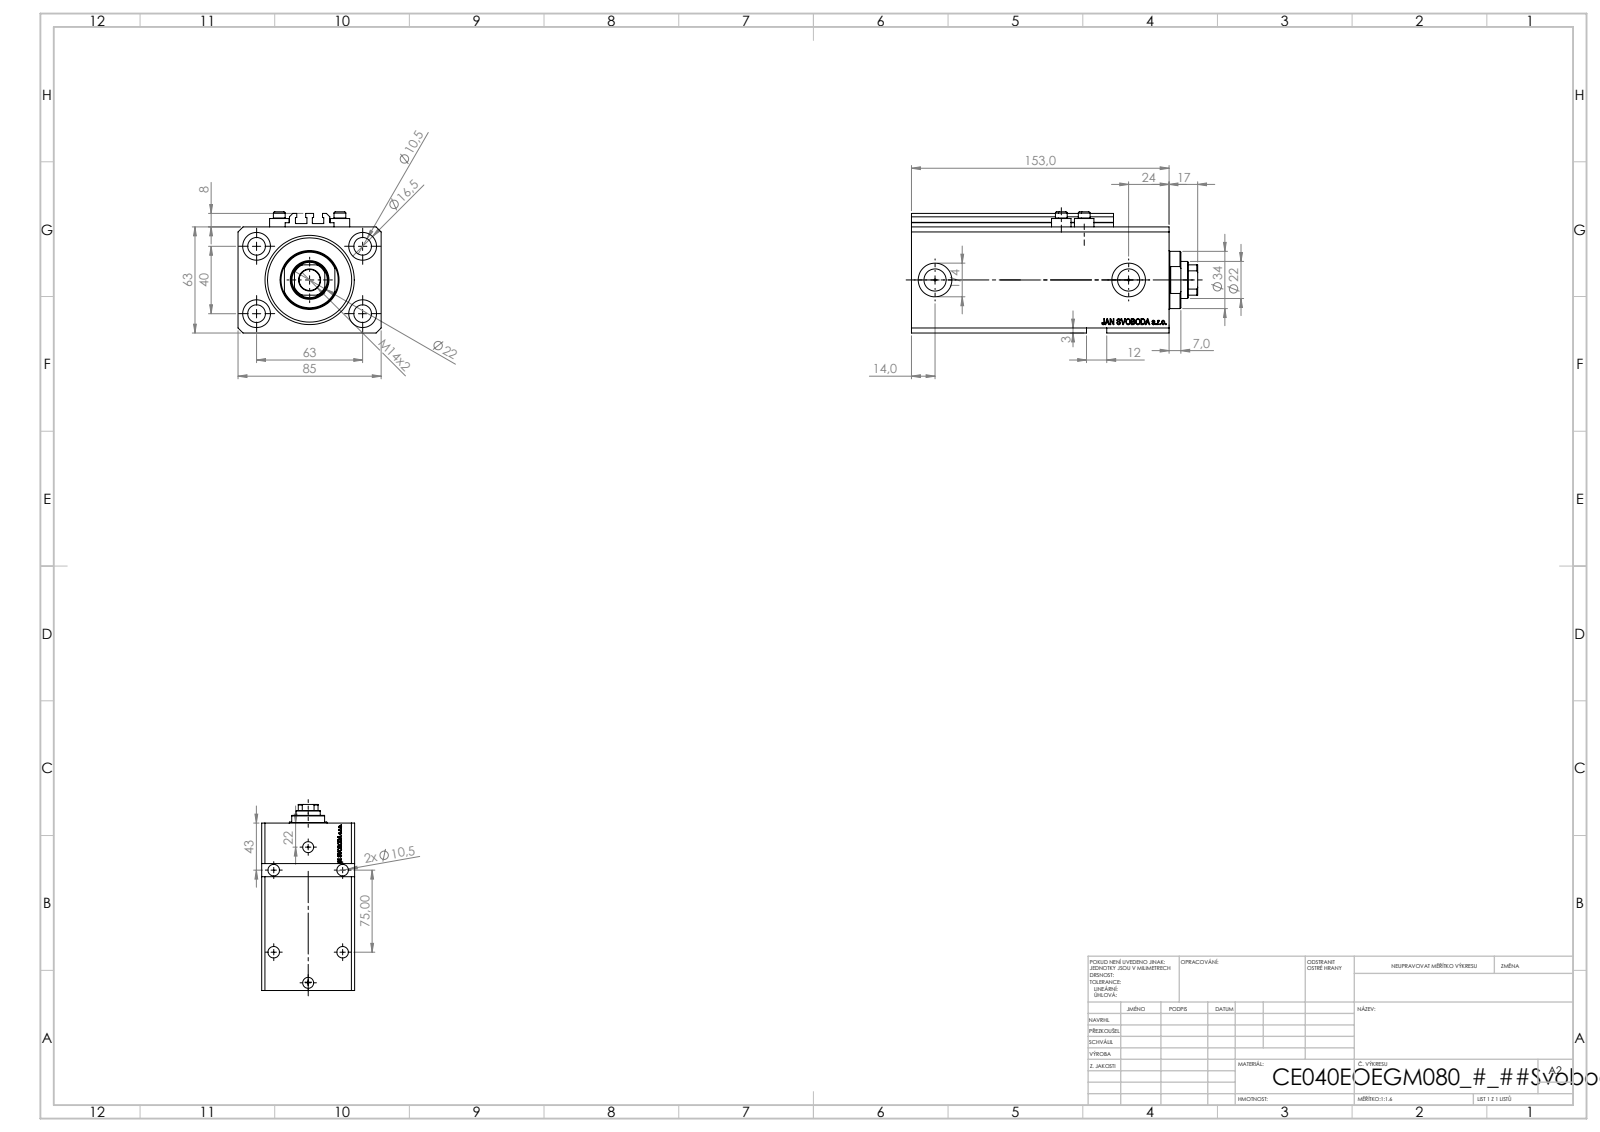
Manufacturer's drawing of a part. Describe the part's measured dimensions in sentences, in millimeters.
The part is named "ALLEN BOLT V250CE; V250CE_VC_E; V250CE_E_Body; V250CE_C_VCP". Its 3-D file was written by "SolidWorks 2019 (CONFIG_CONTROL_DESIGN)". It is 8 solids with 1107 faces: 535 planar, 146 cylindrical and 426 other. Overall it measures 170 by 85 by 72 millimeters. Its volume is 683 849 cubic millimeters and its surface area 140 822 square millimeters. Round holes: 8 of diameter 10.5, 4 of diameter 1.25, 4 of diameter 4, 4 of diameter 16.5, 2 of diameter 10, 2 of diameter 13.16, 2 of diameter 20, 1 of diameter 12.5, 1 of diameter 22, 1 of diameter 40, 1 of diameter 53. Round bosses or shafts: 4 of diameter 11.6, 4 of diameter 7, 1 of diameter 34. Partial cylindrical surfaces (rounded edges, fillets, slot ends): 10 of radius 0.2, 1 of radius 10.5. The main face-to-face distances are 63, 85, 153, 17, 136, 11.4, 124.6, 141.6, 3, 65. The hole center spacings are 37.31, 63, 13.6, 15.4, 24.96, 33.62, 36, 37.86.
